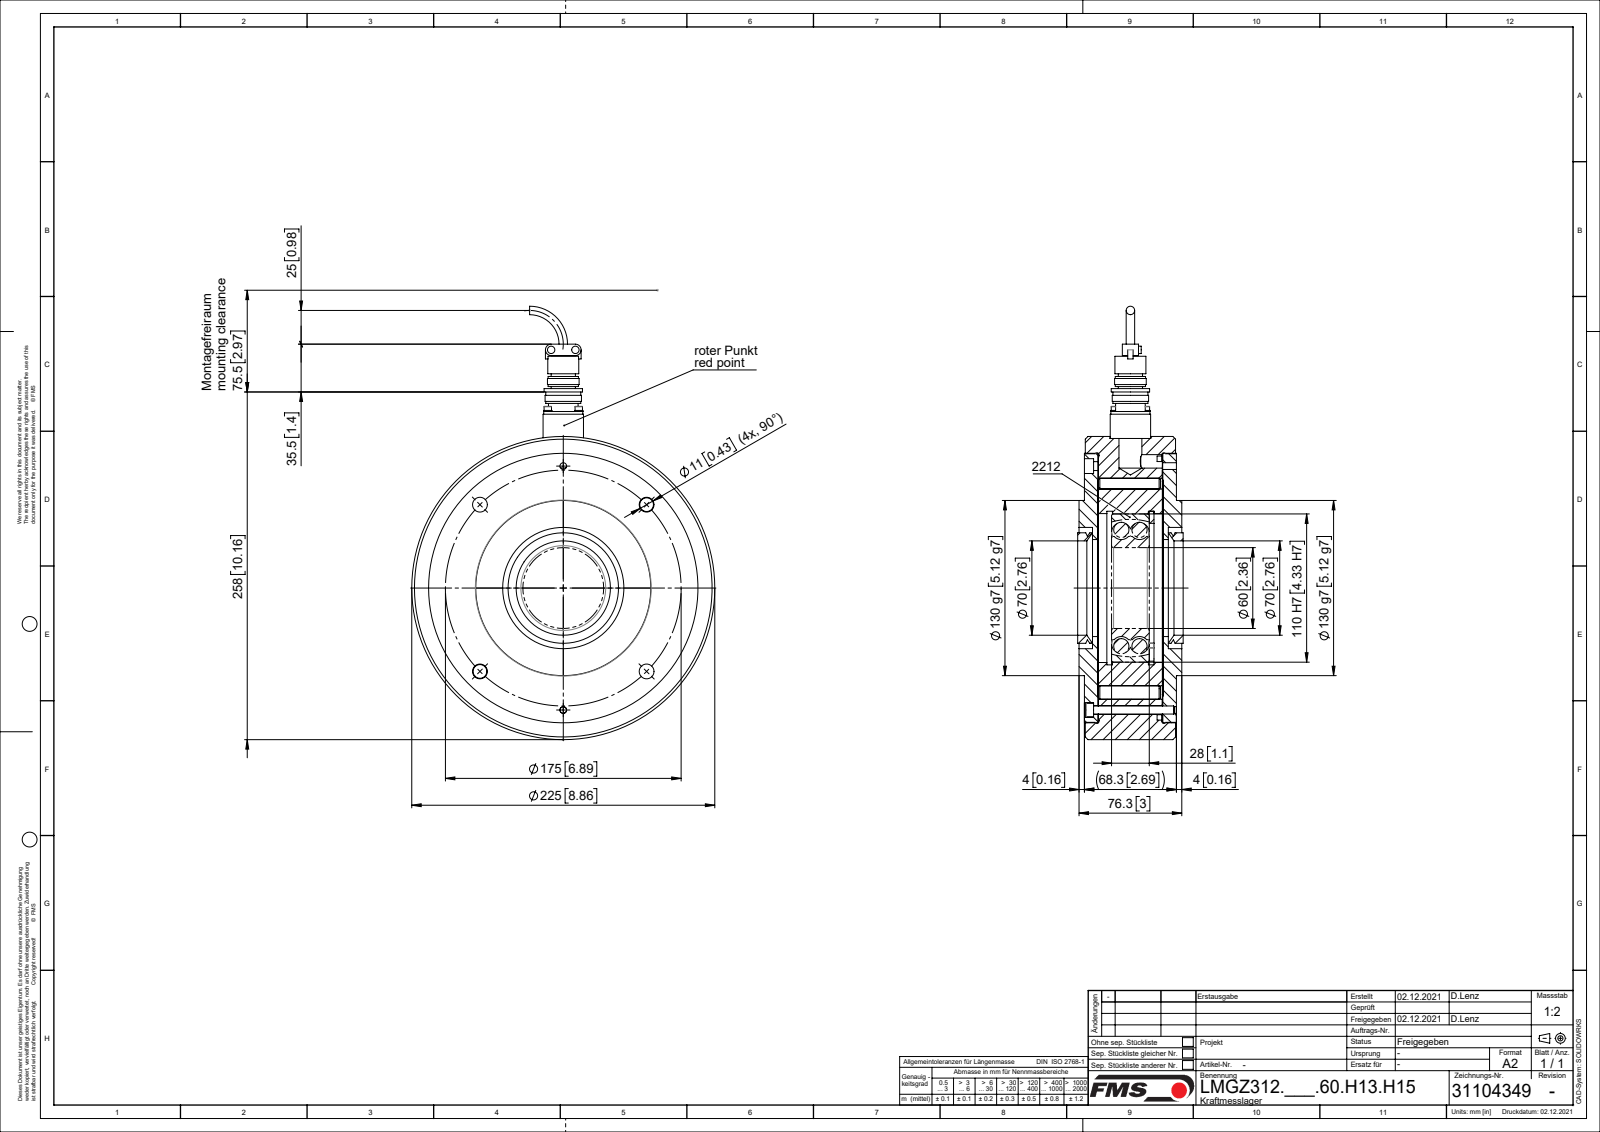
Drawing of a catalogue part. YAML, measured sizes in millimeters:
part_name: "Federringe_DIN127A_M03; Si-Ring DIN472_D110x3.5_spezial; PKL_2212_01; 31101677_V-070A (+8 more)"
step_written_by: "SolidWorks 2018 (CONFIG_CONTROL_DESIGN)"
units: millimeters
bodies: {solids: 51, faces: 583, planar: 149, cylindrical: 280, other: 154}
overall_size: [321.65, 225, 78.3]
volume: 2241000
surface_area: 437158
round_holes:
  - {diameter: 11, count: 6}
  - {diameter: 2.5, count: 4}
  - {diameter: 3.1, count: 4}
  - {diameter: 3.4, count: 4}
  - {diameter: 22, count: 4}
  - {diameter: 3.5, count: 2}
  - {diameter: 5, count: 2}
  - {diameter: 6.6, count: 2}
  - {diameter: 10, count: 2}
  - {diameter: 10.2, count: 2}
  - {diameter: 8, count: 1}
  - {diameter: 17, count: 1}
round_bosses_or_shafts:
  - {diameter: 5.5, count: 6}
  - {diameter: 6.2, count: 4}
  - {diameter: 3, count: 4}
  - {diameter: 2.5, count: 4}
  - {diameter: 225, count: 1}
  - {diameter: 200, count: 1}
  - {diameter: 199, count: 1}
  - {diameter: 188, count: 1}
partial_cylinders:
  - {radius: 0.1, count: 4}
  - {radius: 4.25, count: 2}
  - {radius: 5.81, count: 2}
  - {radius: 46.6, count: 1}
  - {radius: 79, count: 1}
  - {radius: 86, count: 1}
face_to_face_distances: [10.45, 47.65, 9.7, 48.15, 10.2, 57.85, 58.1, 0.5, 58.6, 0.75]
hole_center_spacings: [16.26, 23, 63.81, 68.17, 84, 87.5, 123.74, 152.49]
